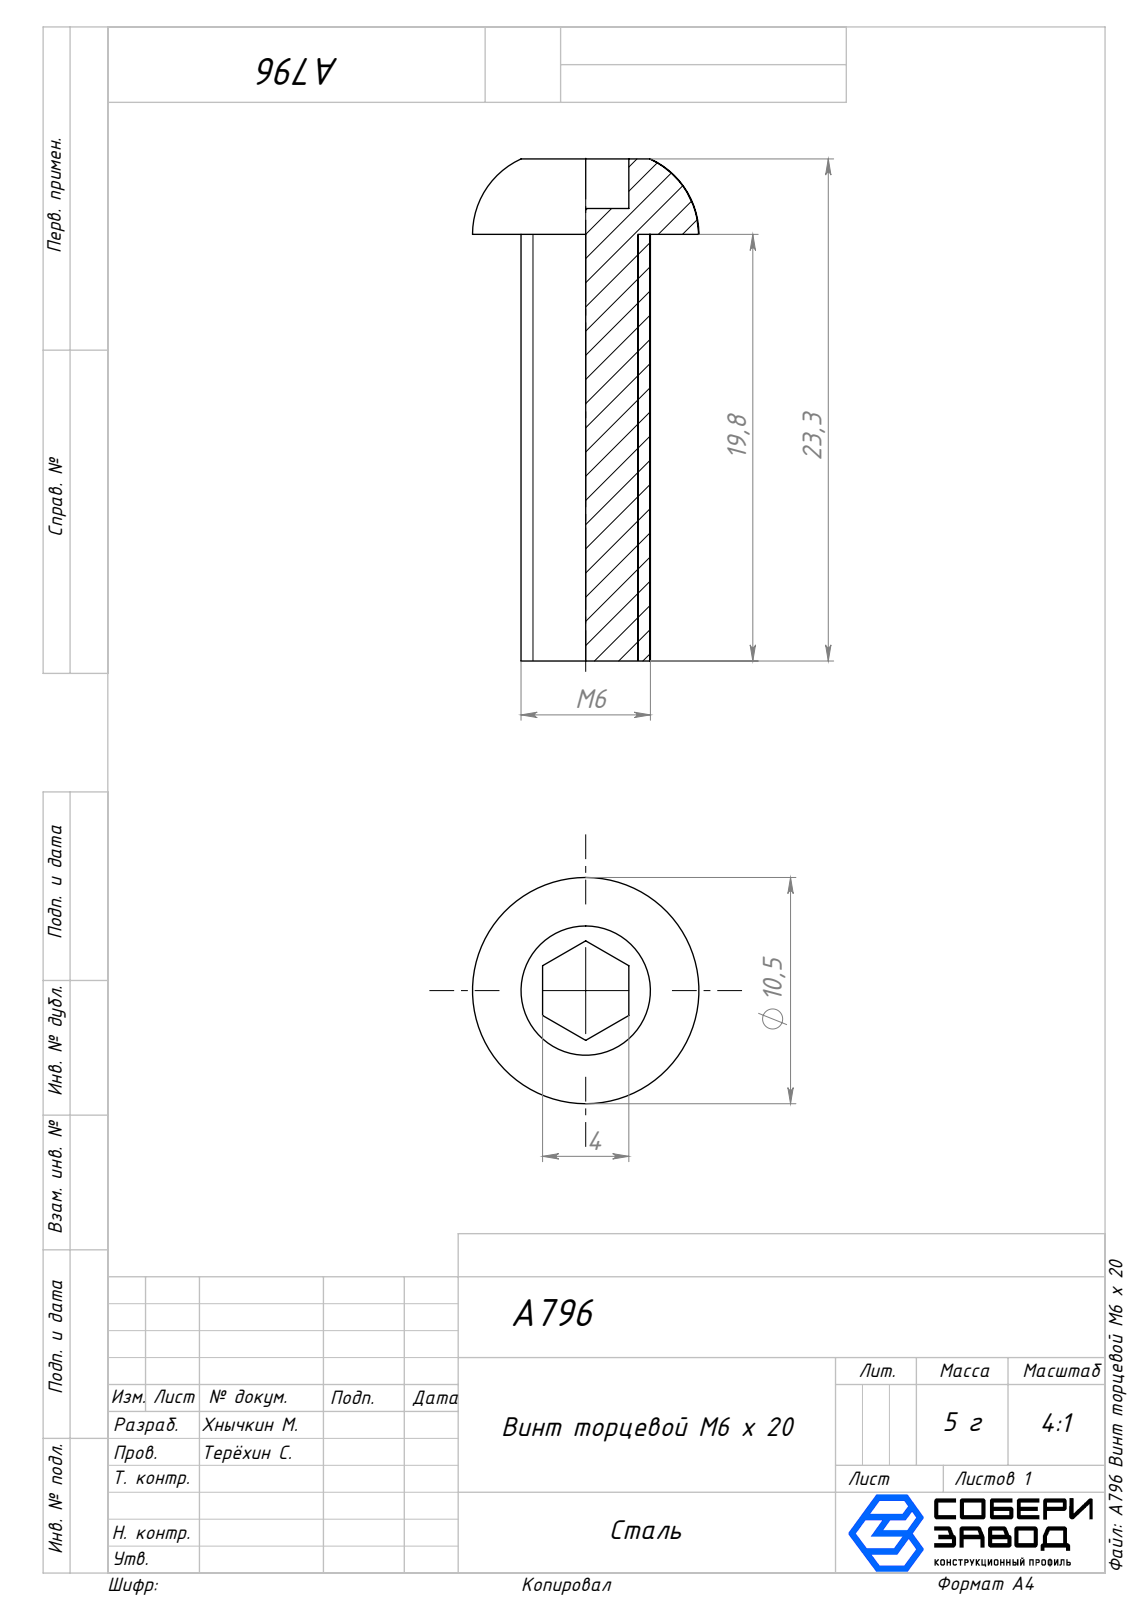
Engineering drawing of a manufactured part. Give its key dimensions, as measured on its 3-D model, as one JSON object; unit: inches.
{"part_name": "A796 Винт торцевой М6 х 20", "step_written_by": "SolidWorks 2025 (AUTOMOTIVE_DESIGN)", "units": "inches", "bodies": {"solids": 1, "faces": 14, "planar": 10, "cylindrical": 2, "other": 2}, "overall_size": [0.917, 0.413, 0.413], "volume_in3": 0.047, "surface_area_in2": 0.997, "round_bosses_or_shafts": [[0.236, 1]], "face_to_face_distances": [0.78, 0.157, 0.917, 0.138, 0.827, 0.047, 0.091]}
